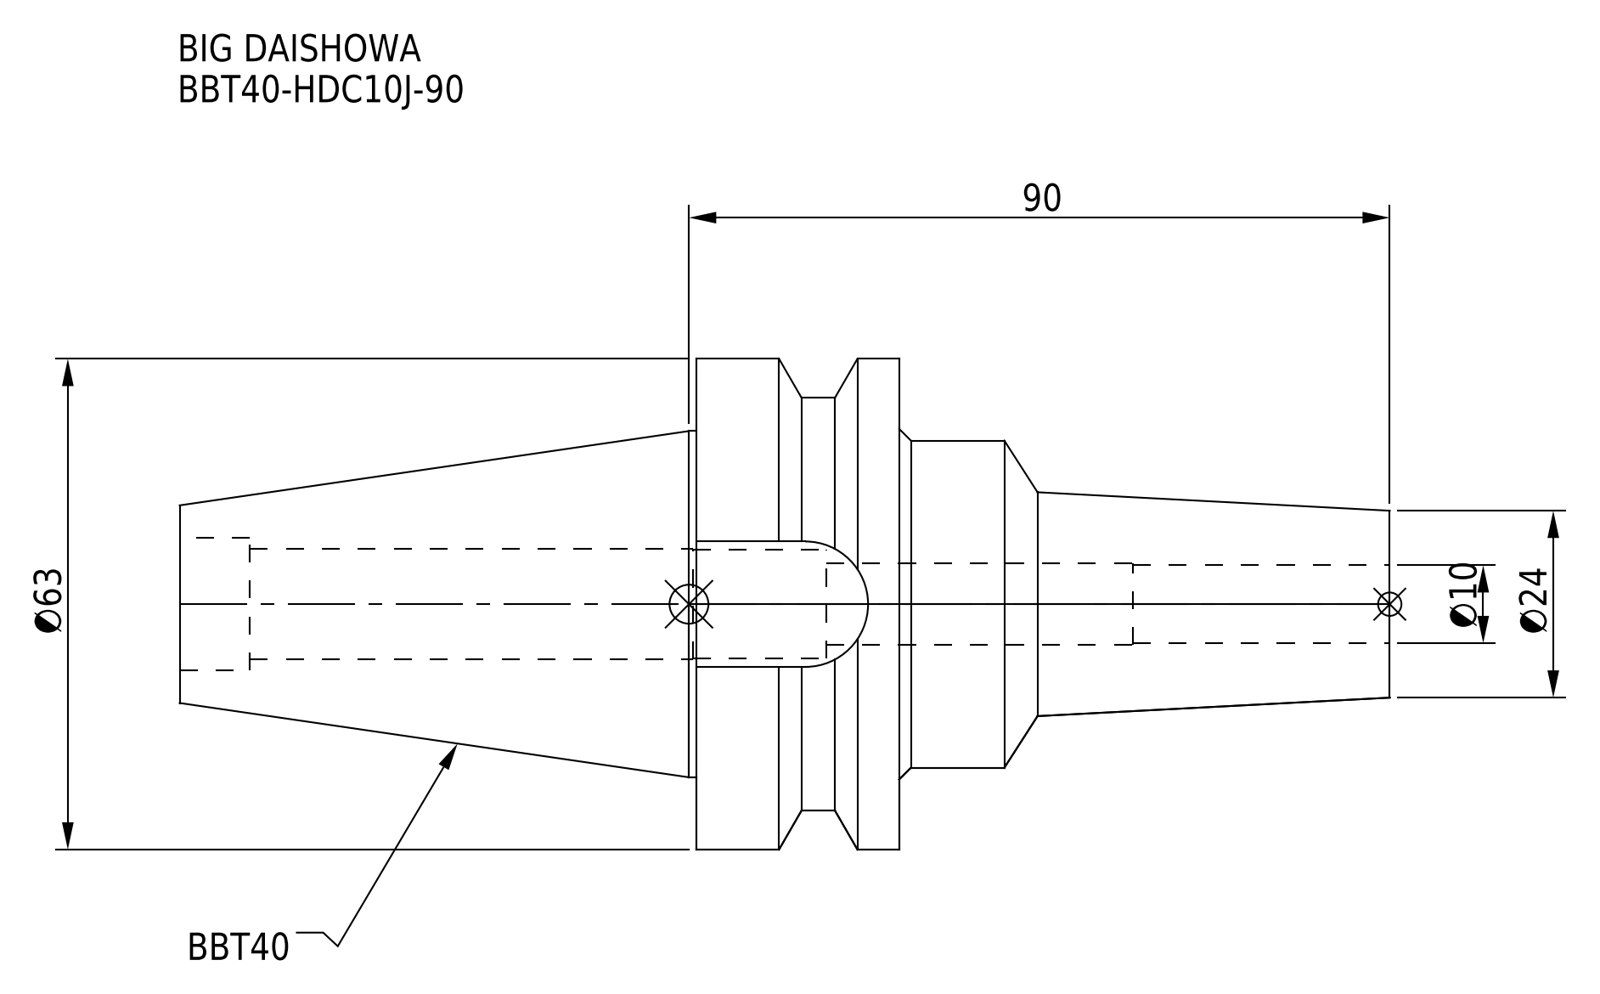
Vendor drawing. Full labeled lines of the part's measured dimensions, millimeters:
Part name (STEP PRODUCT): BBT40-HDC10J-90
STEP written by: CREO PARAMETRIC BY PTC INC, 2016380 (AUTOMOTIVE_DESIGN)
Units: millimetres
Bodies: 1 solid, 50 faces (14 planar, 24 cylindrical, 12 other)
Overall size (bounding box): 155.4 × 63 × 63
Volume: 163 757 mm³ · Surface area: 30 126 mm²
Round holes (diameter × count): ⌀10 ×1, ⌀10.5 ×1, ⌀14 ×1, ⌀14.2 ×1, ⌀17 ×1
Round bosses / shafts (diameter × count): ⌀63 ×1, ⌀53 ×1, ⌀44.45 ×1, ⌀42 ×1
Partial cylindrical surfaces — rounded edges, fillets, slot ends (radius × count): R8.05 ×1
Main face-to-face distances: 26, 63, 89, 45, 155.4, 92.4, 66.4, 16.1, 146.4, 83.4
